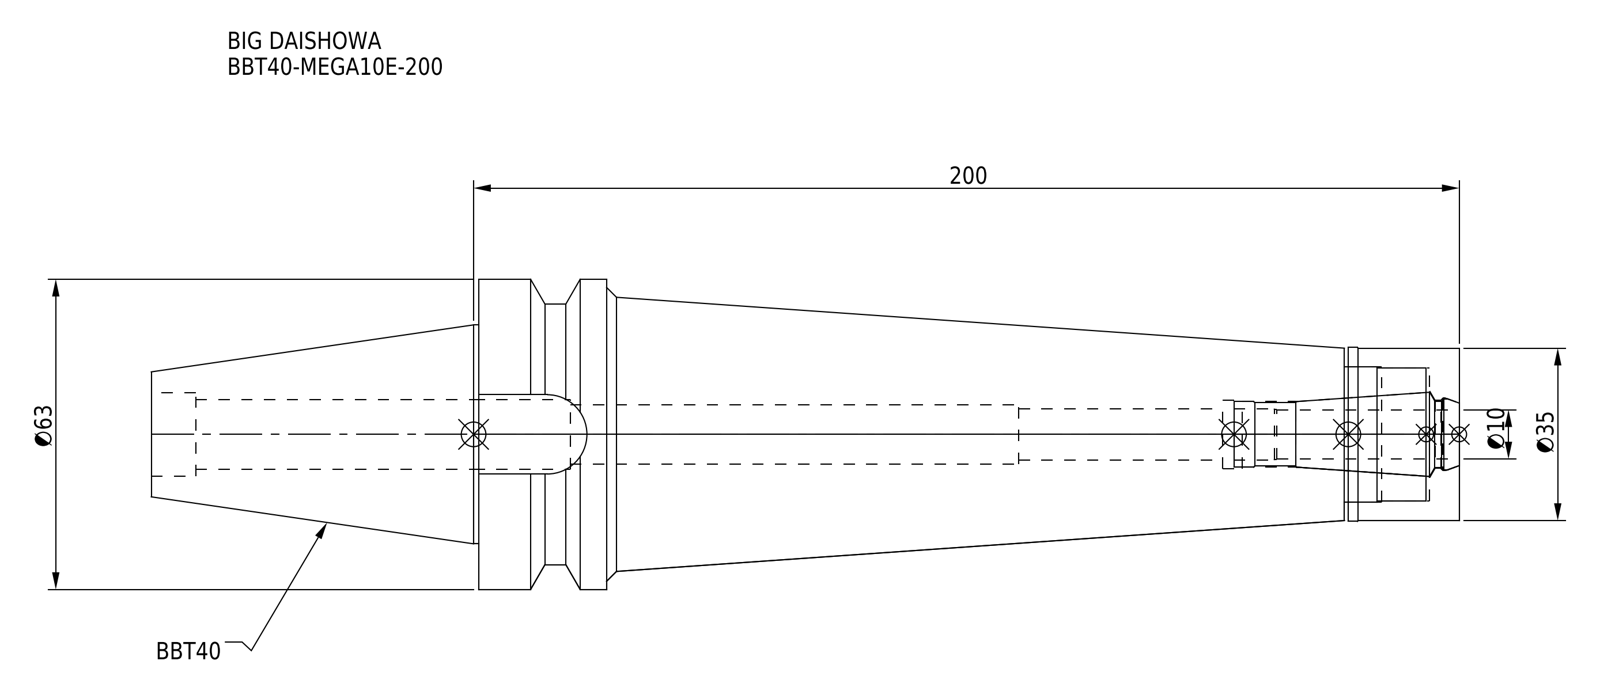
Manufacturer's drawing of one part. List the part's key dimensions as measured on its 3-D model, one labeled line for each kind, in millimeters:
Part name (STEP PRODUCT): MEN10_1.stp; DXF_TEMP_ASSY_ASM_4_ASM.stp; BBT40-MEGA10E-200_1.stp; BBT40-MEGA10E-200-100.stp (+3 more)
STEP written by: SolidWorks 2019 (CONFIG_CONTROL_DESIGN)
Units: millimetres
Bodies: 2 solids, 81 faces (21 planar, 40 cylindrical, 20 other)
Overall size (bounding box): 265.4 × 63 × 63
Volume: 369 255 mm³ · Surface area: 56 108 mm²
Round holes (diameter × count): ⌀10.4 ×1, ⌀12 ×1, ⌀13.3 ×1, ⌀13.8 ×1, ⌀13.9 ×1, ⌀14.2 ×1, ⌀14.7 ×1, ⌀17 ×1, ⌀27 ×1, ⌀27.5 ×1
Round bosses / shafts (diameter × count): ⌀63 ×1, ⌀53 ×1, ⌀44.45 ×1, ⌀35.3 ×1, ⌀35 ×1
Partial cylindrical surfaces — rounded edges, fillets, slot ends (radius × count): R8.05 ×1
Main face-to-face distances: 199, 22.5, 176.5, 23.3, 0.8, 175.7, 167, 6.7, 15.8, 16.6
